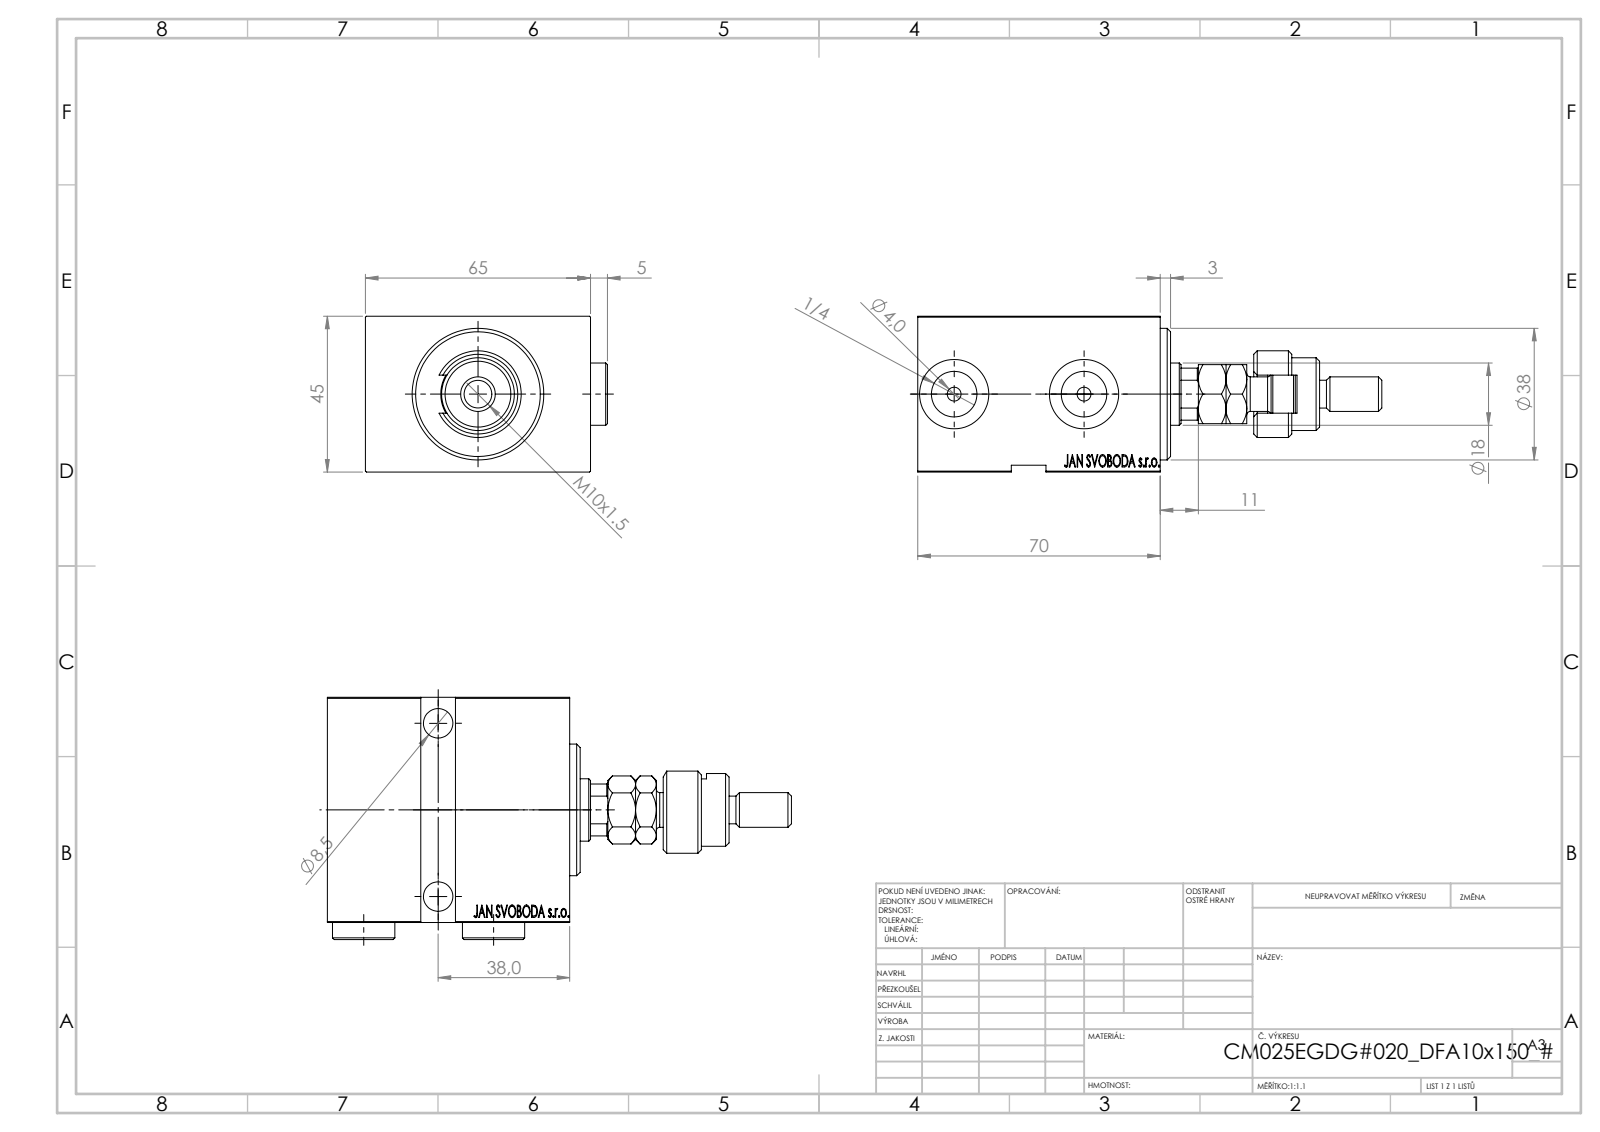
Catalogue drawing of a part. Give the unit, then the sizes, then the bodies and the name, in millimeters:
Units: millimetres
Overall size (bounding box): 134 × 69.9 × 45
Round holes (diameter × count): ⌀8.5 ×3, ⌀4 ×2, ⌀13.16 ×2, ⌀13.5 ×2, ⌀20 ×2, ⌀18 ×1, ⌀21.5 ×1, ⌀35 ×1
Round bosses / shafts (diameter × count): ⌀18 ×2, ⌀38 ×1, ⌀27 ×1, ⌀25 ×1, ⌀21 ×1, ⌀16 ×1, ⌀10 ×1, ⌀8 ×1
Partial cylindrical surfaces — rounded edges, fillets, slot ends (radius × count): R5.5 ×1, R8.5 ×1, R8.75 ×1
Main face-to-face distances: 45, 65, 70, 5, 8, 3, 64.9, 6, 2, 64
Hole centre spacings: 37.5, 50
Volume: 201 854 mm³ · Surface area: 48 471 mm²
Bodies: 7 solids, 985 faces (470 planar, 73 cylindrical, 442 other)
Part name (STEP PRODUCT): V450CM_VC_B; Zatka_OIL_PORT; FEMALE_PART_FOR_DFA; V450CM_E_Body (+2 more)
STEP written by: SolidWorks 2019 (CONFIG_CONTROL_DESIGN)
